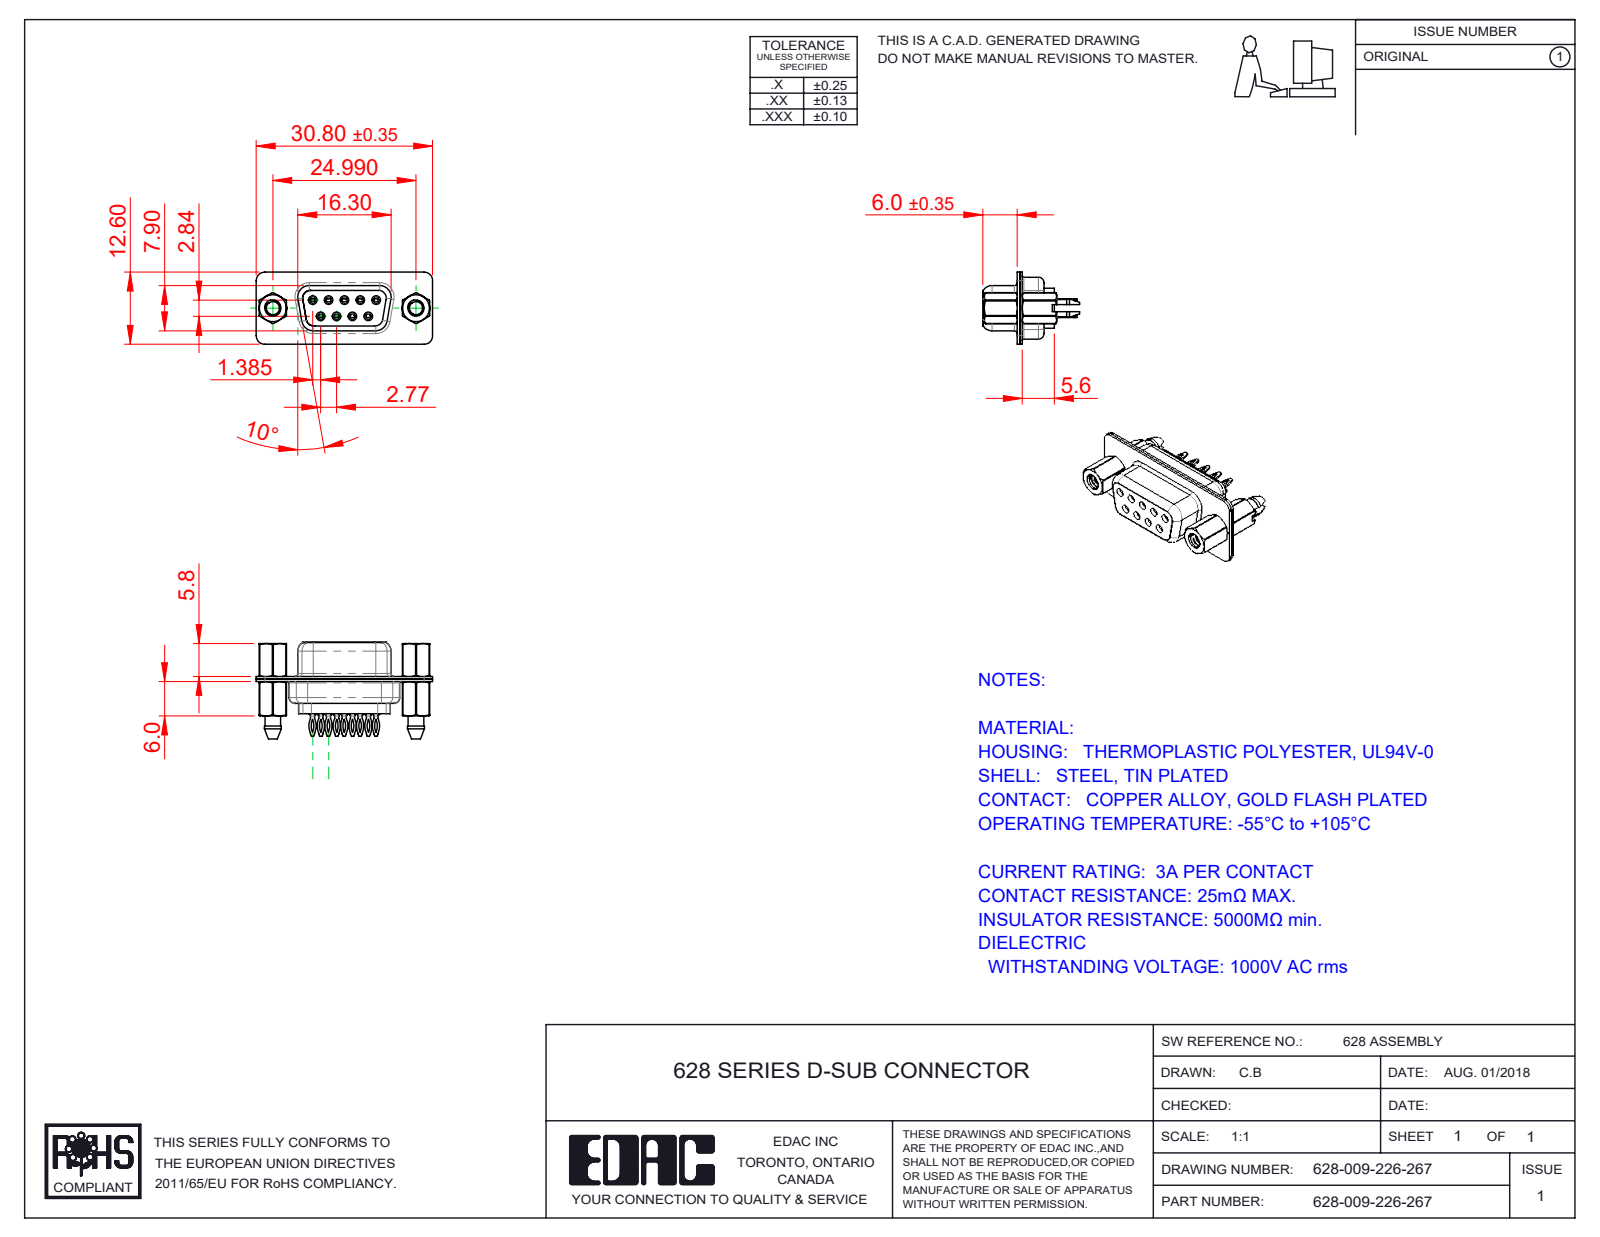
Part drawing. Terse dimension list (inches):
name: 628 4-40 Threaded Boardlock_LP; 628 Shell Front_09 Contacts; 628 Housing_09 LP; 628-009-226-267 (+4 more)
written by: SolidWorks 2020 (CONFIG_CONTROL_DESIGN)
unit: in
bodies: 16 solids, 1388 faces (364 planar, 484 cylindrical, 540 other)
size: 1.213 × 0.665 × 0.496
volume: 0.127 in³; area: 8.139 in²
holes: 9× ⌀0.031, 9× ⌀0.035, 9× ⌀0.043, 9× ⌀0.063, 5× ⌀0.067, 2× ⌀0.089, 2× ⌀0.09, 2× ⌀0.157, 2× ⌀0.159, 2× ⌀0.191
bosses: 9× ⌀0.079, 9× ⌀0.059, 9× ⌀0.047, 2× ⌀0.195, 2× ⌀0.189, 2× ⌀0.11
rounds: 19× R0.059, 18× R0.115, 18× R0.131, 12× R0.079, 9× R0.011, 6× R0.053, 6× R0.063, 4× R0.01
face distances: 0.018, 0.016, 0.035, 0.075, 0.335, 0.26, 0.055, 0.492, 0.187, 0.02
hole spacings: 0.124, 0.109, 0.218, 0.198, 0.198, 0.327, 0.294, 0.295
